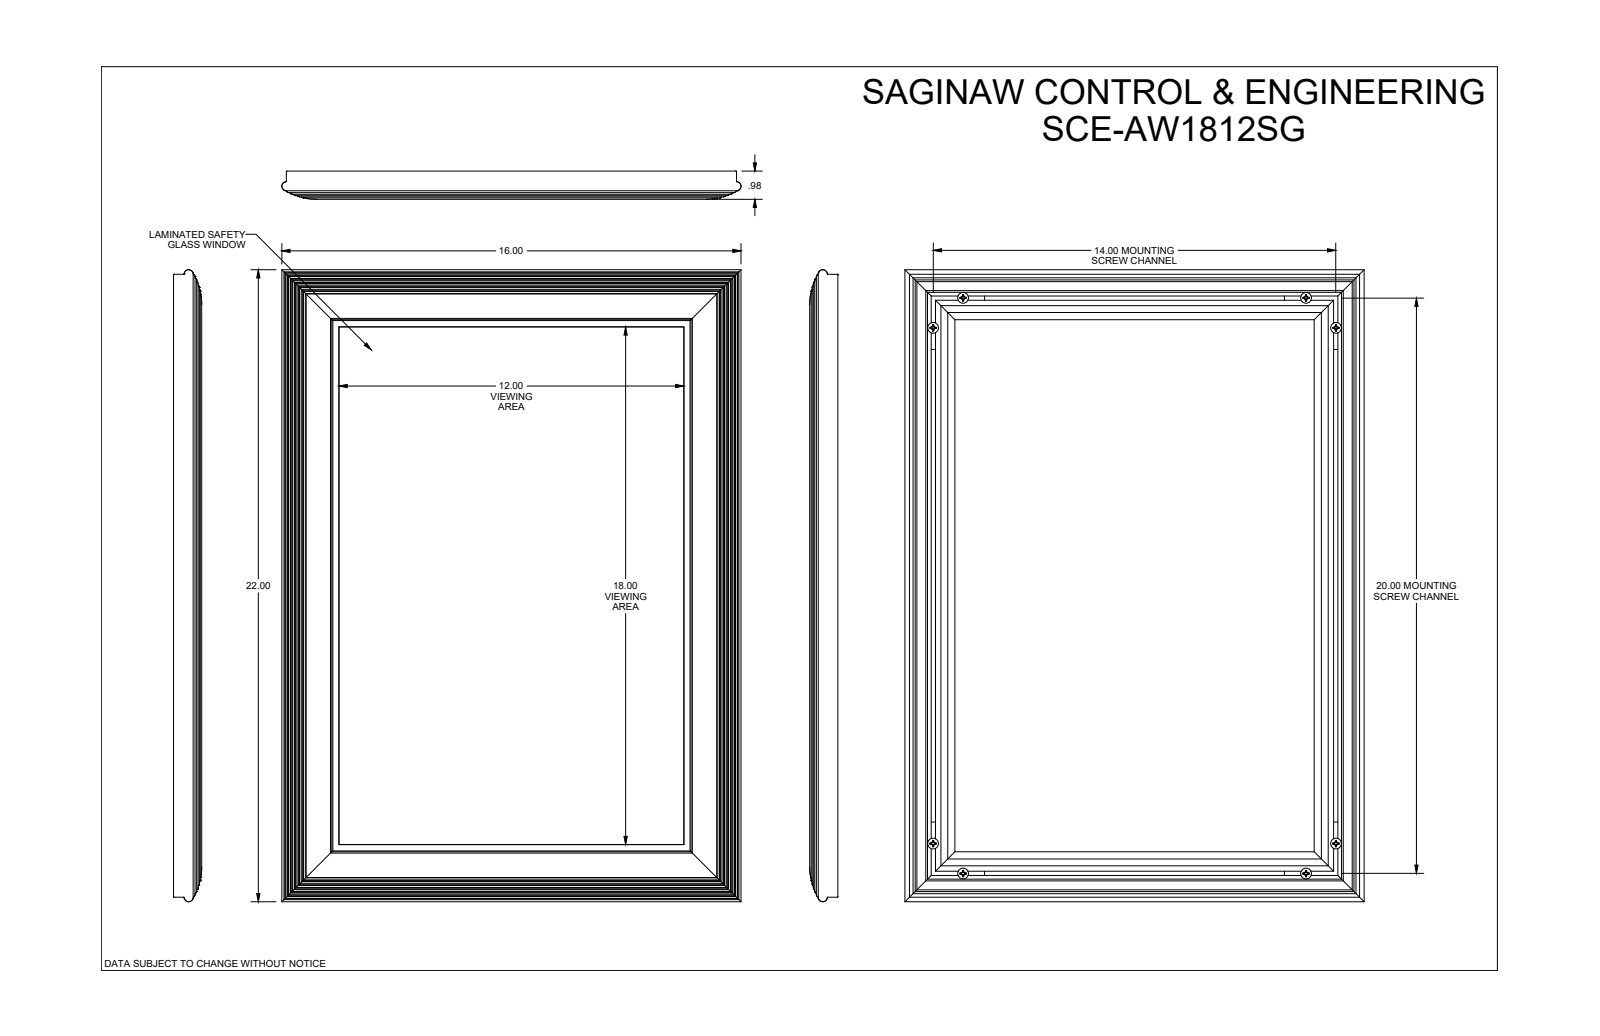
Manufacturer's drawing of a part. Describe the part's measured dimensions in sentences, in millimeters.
The part is named "SCE-AW1812SG". Its 3-D file was written by "SolidWorks 2021 (AUTOMOTIVE_DESIGN)". It is 25 solids with 1202 faces: 454 planar, 308 cylindrical and 440 other. Overall it measures 558.2 by 405.8 by 24.9 millimeters. Its volume is 1 592 000 cubic millimeters and its surface area 967 700 square millimeters. Round holes: 8 of diameter 3.8, 4 of diameter 4.2. Round bosses or shafts: 8 of diameter 4.8, 8 of diameter 3.1. Partial cylindrical surfaces (rounded edges, fillets, slot ends): 156 of radius 0.5, 24 of radius 1.5, 16 of radius 0.3, 12 of radius 0.8, 4 of radius 0.4, 4 of radius 0.5, 4 of radius 1.5, 4 of radius 4. The main face-to-face distances are 6, 1.5, 1.7, 1.9, 5.5, 0.5, 3.2, 38.6, 14.3, 8. The hole center spacings are 37.4, 330.6, 482.7, 583.8, 303, 356, 455.4, 508.4.
